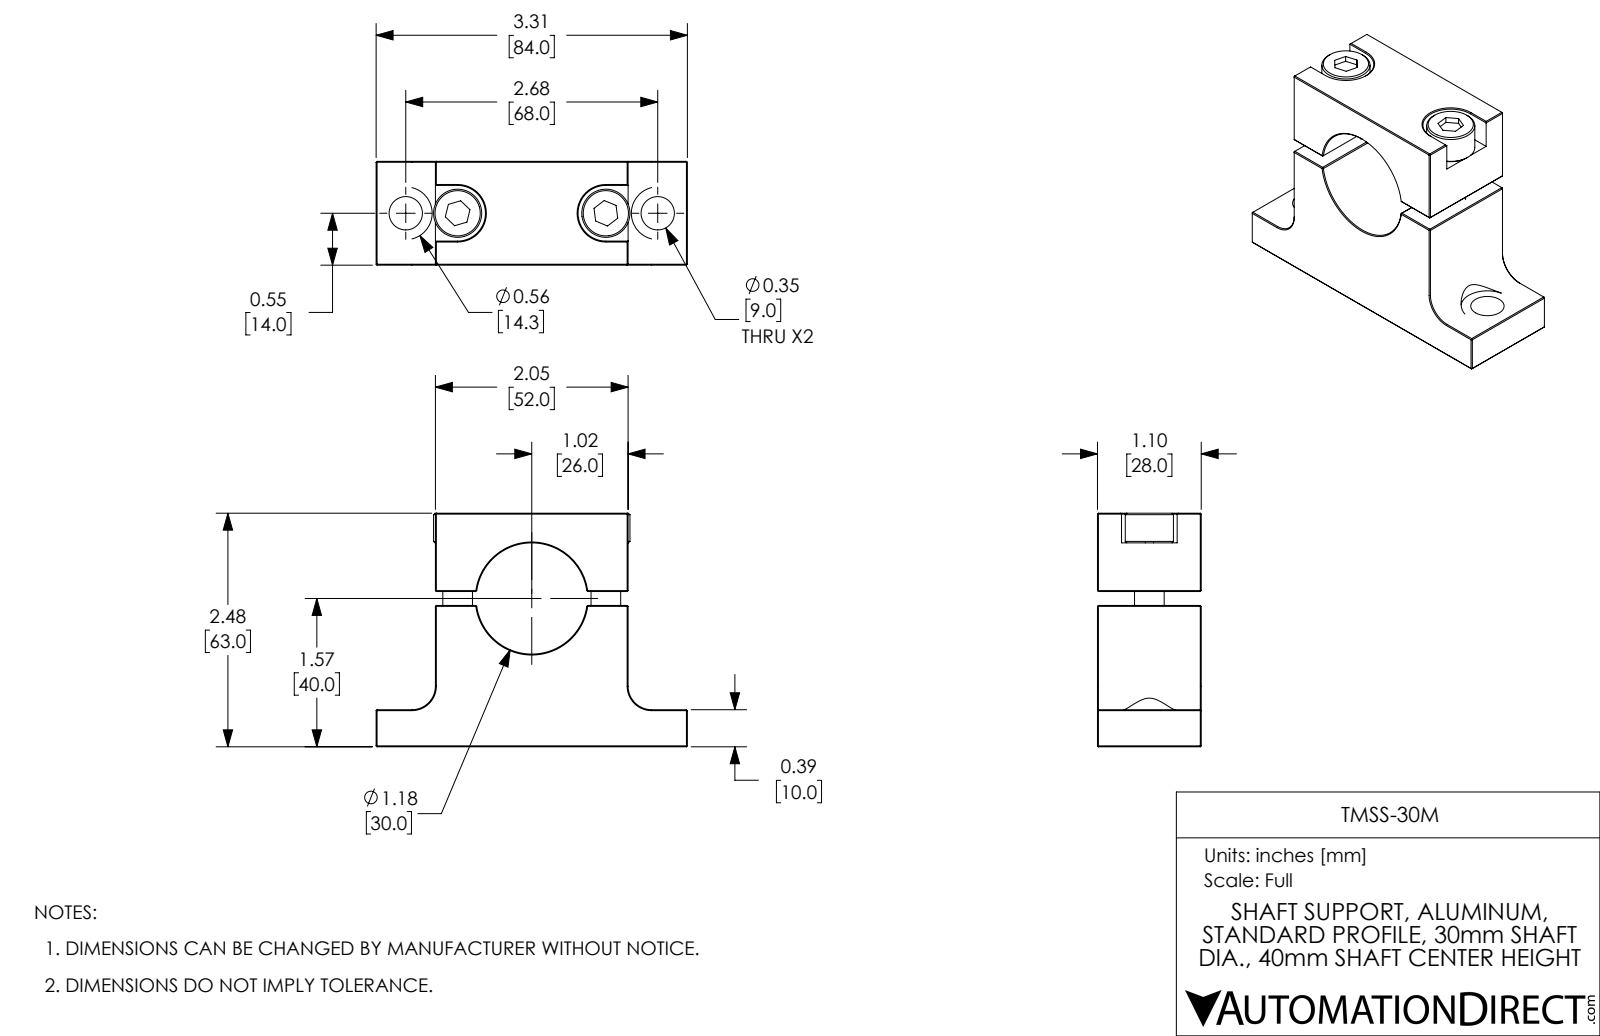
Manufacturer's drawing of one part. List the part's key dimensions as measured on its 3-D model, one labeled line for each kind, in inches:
Part name (STEP PRODUCT): TMSS-30M
STEP written by: SolidWorks 2017 (AUTOMOTIVE_DESIGN)
Units: inches
Bodies: 4 solids, 175 faces (120 planar, 31 cylindrical, 24 other)
Overall size (bounding box): 3.307 × 2.48 × 1.102
Volume: 4.585 in³ · Surface area: 34.67 in²
Round holes (diameter × count): ⌀0.262 ×2, ⌀0.354 ×2, ⌀0.394 ×2, ⌀0.094 ×1, ⌀1.181 ×1
Round bosses / shafts (diameter × count): ⌀0.512 ×2, ⌀0.315 ×2
Partial cylindrical surfaces — rounded edges, fillets, slot ends (radius × count): R0.25 ×2, R0.281 ×2, R0.296 ×2
Main face-to-face distances: 1.102, 2.48, 2.047, 0.63, 2.677, 1.501, 0.98, 0.394, 1.107, 2.087
Hole centre spacings: 0.551, 0.787, 1.339, 2.126, 1.575, 2.677
